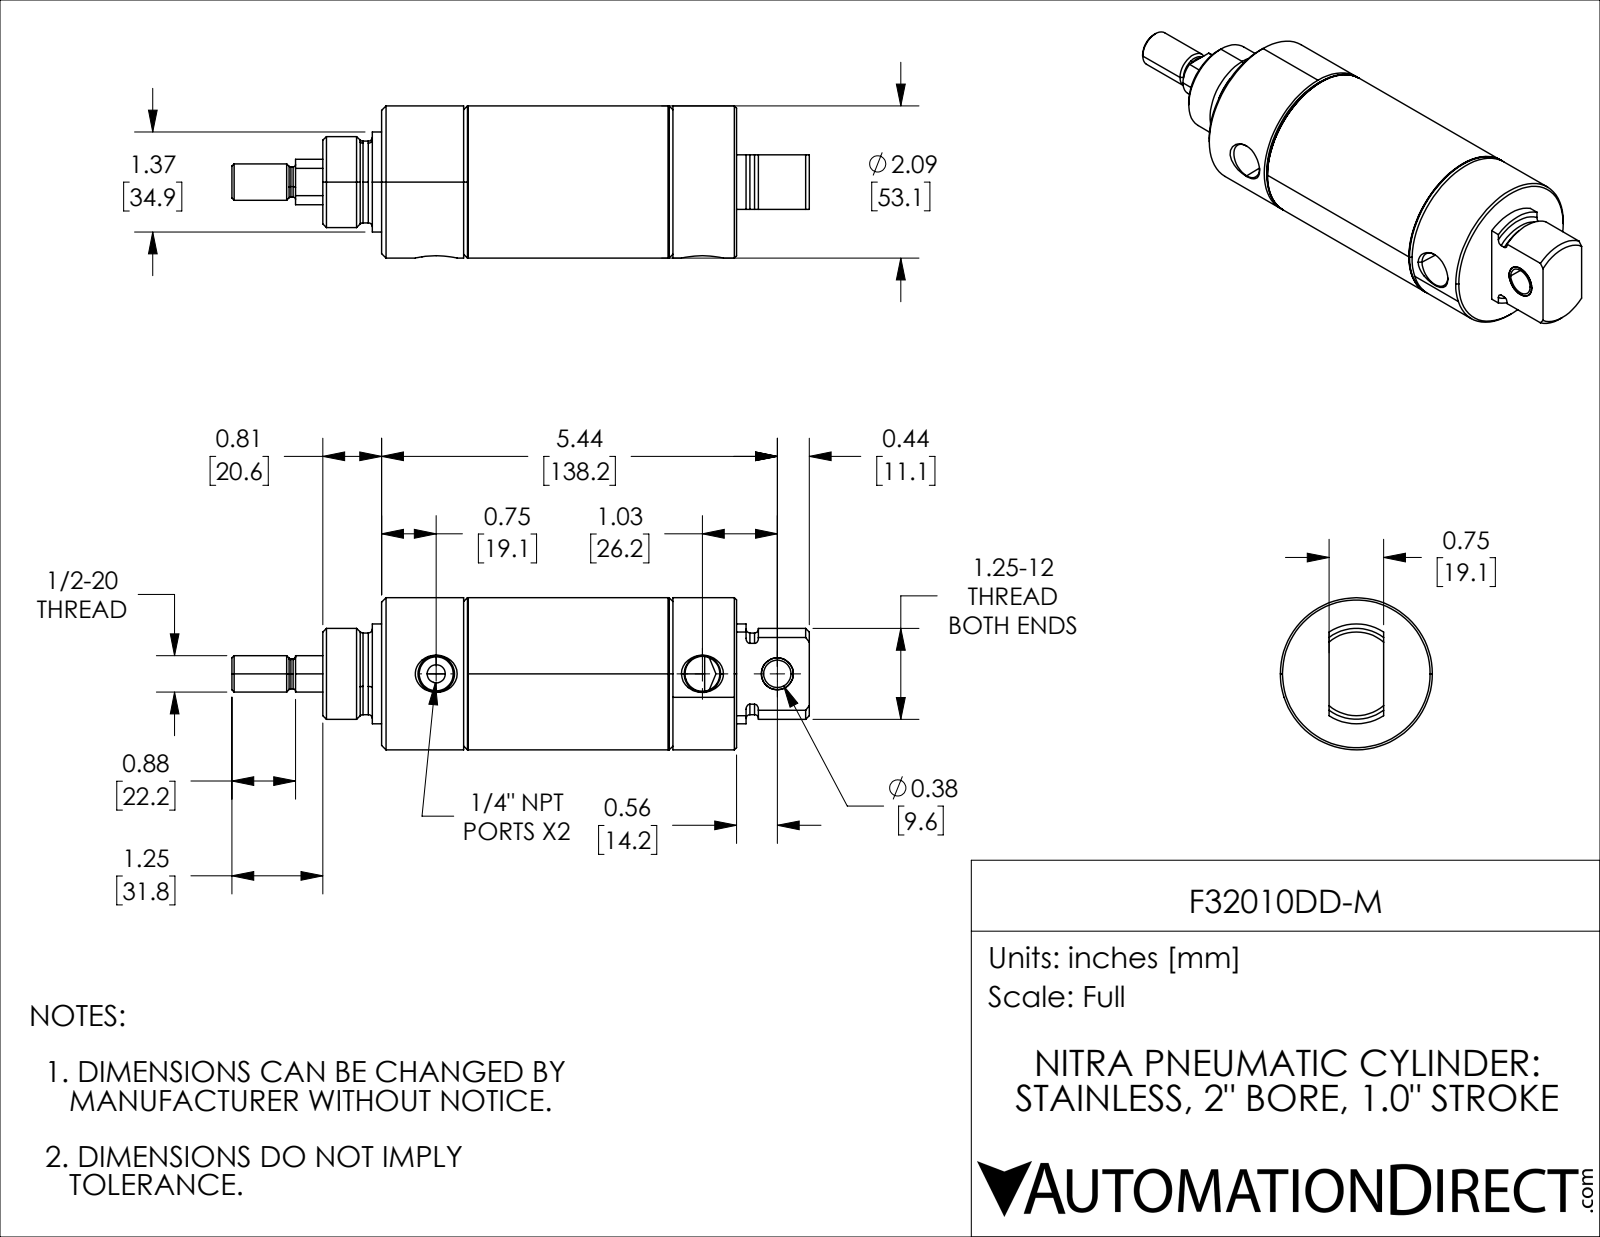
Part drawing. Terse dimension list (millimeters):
name: F32010DD-M_9; F32010DD-M; F32010DD-M_11; F32010DD-M_7 (+2 more)
written by: SolidWorks 2021 (CONFIG_CONTROL_DESIGN)
unit: mm
bodies: 5 solids, 160 faces (31 planar, 60 cylindrical, 69 other)
size: 201.62 × 53.09 × 53.09
volume: 244 803 mm³; area: 71 637 mm²
holes: 1× ⌀6.35, 1× ⌀9.55, 1× ⌀11.15, 1× ⌀12.18, 1× ⌀16.52, 1× ⌀19.05, 1× ⌀49.05
bosses: 1× ⌀53.09, 1× ⌀51.16, 1× ⌀34.87, 1× ⌀31.75, 1× ⌀28.51, 1× ⌀15.88, 1× ⌀12.7, 1× ⌀10.46
rounds: 1× R14.25
face distances: 55.58, 30.18, 25.4, 55.57, 85.8, 60.4, 30.22, 30.17, 30.23, 38.15
hole spacings: 26.17, 92.96, 119.13
